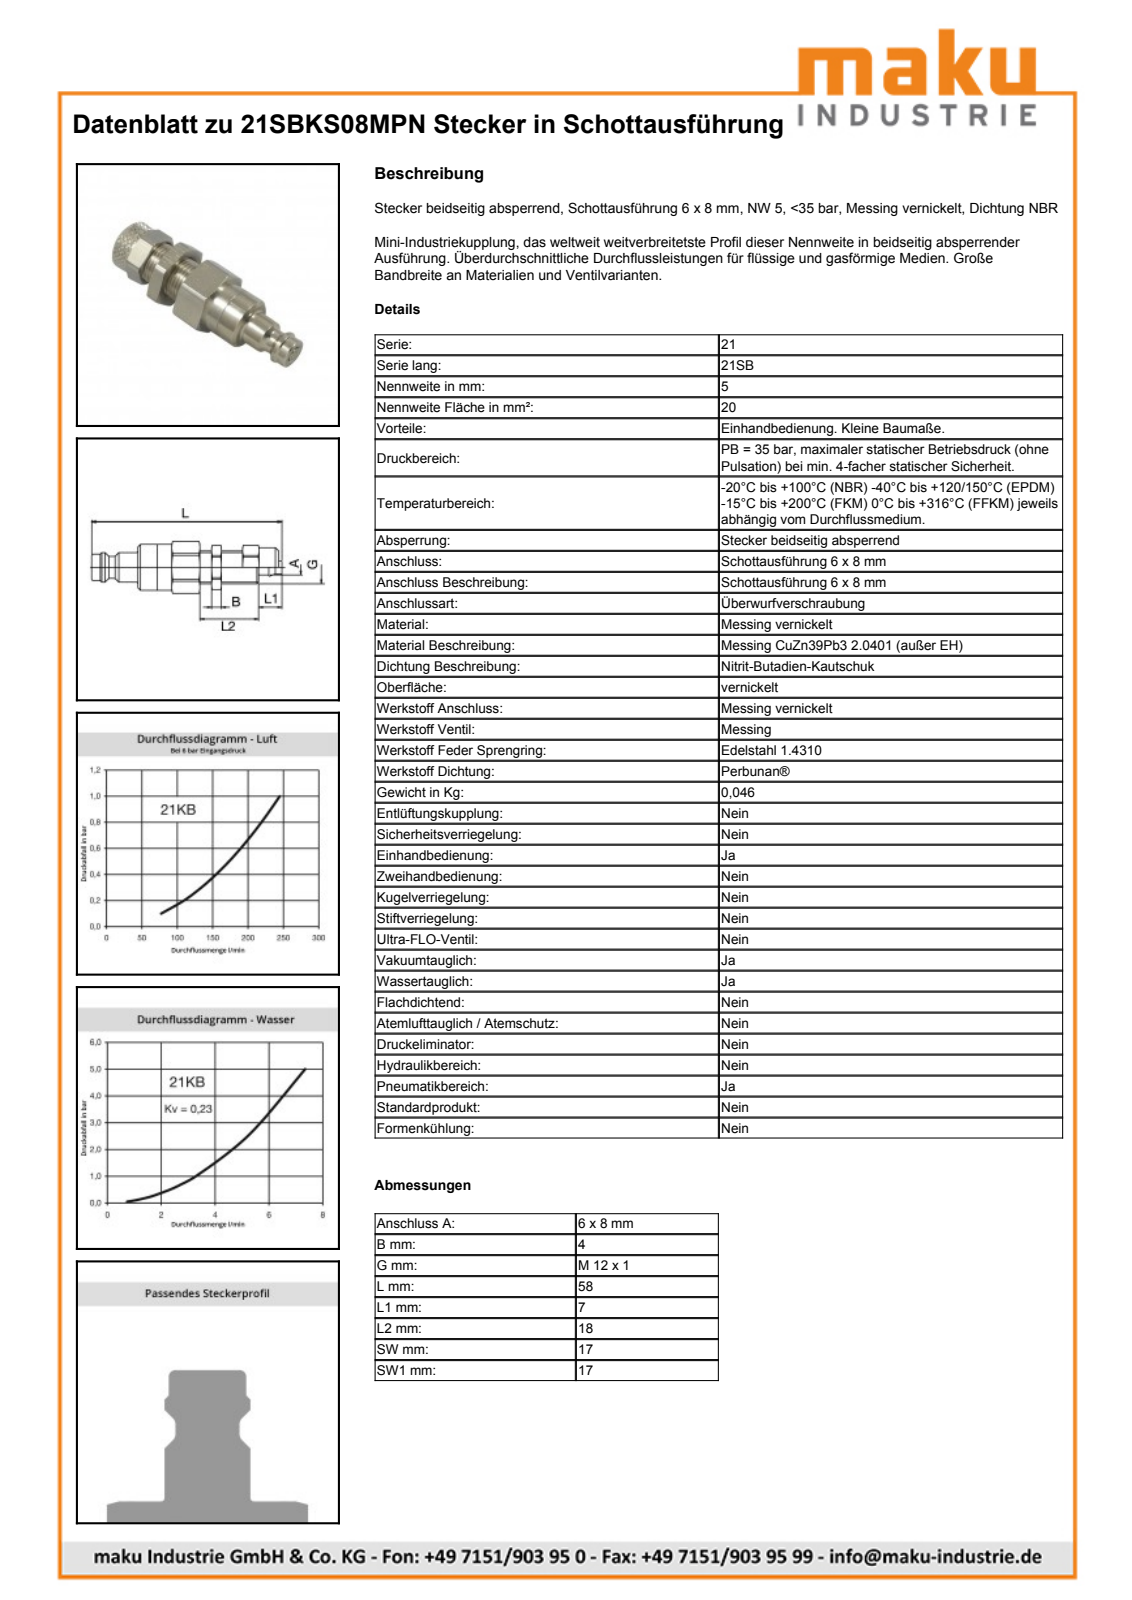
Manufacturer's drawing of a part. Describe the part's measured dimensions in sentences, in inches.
The part is named "D108236". Its 3-D file was written by "Autodesk Inventor 2013 (AUTOMOTIVE_DESIGN)". It is 1 solid with 129 faces: 33 planar, 36 cylindrical and 60 other. Overall it measures 2.283 by 0.751 by 0.744 inches. Its volume is 0.477 cubic inches and its surface area 6.941 square inches. Round holes: 1 of diameter 0.411, 1 of diameter 0.433, 1 of diameter 0.472, 1 of diameter 0.476, 1 of diameter 0.492. Round bosses or shafts: 1 of diameter 0.551, 1 of diameter 0.427, 1 of diameter 0.408, 1 of diameter 0.354, 1 of diameter 0.319, 1 of diameter 0.264, 1 of diameter 0.238. Partial cylindrical surfaces (rounded edges, fillets, slot ends): 1 of radius 0.305, 1 of radius 0.377. The main face-to-face distances are 0.669, 0.157, 0.551, 0.423, 0.266, 0.337, 0.602, 0.76, 1.299, 1.041.
